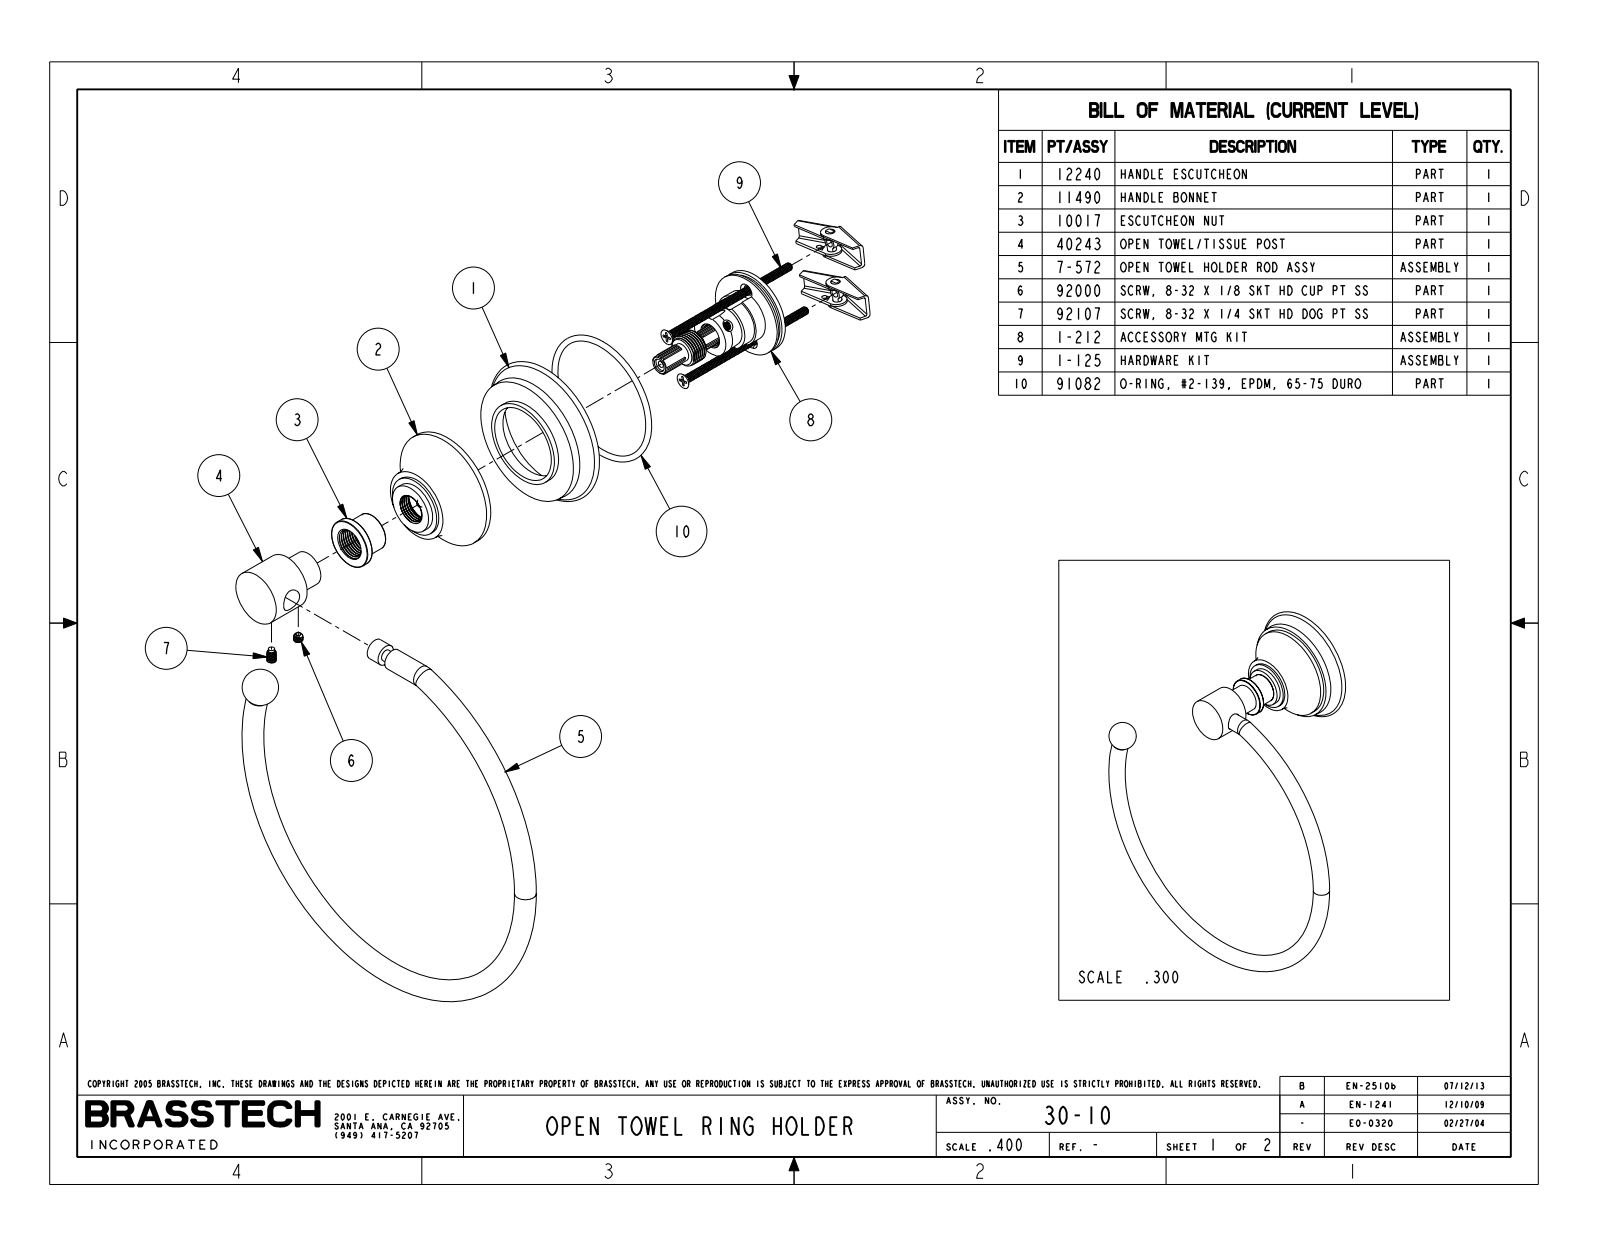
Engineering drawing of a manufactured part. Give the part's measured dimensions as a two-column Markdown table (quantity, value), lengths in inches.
| quantity | value |
| --- | --- |
| part name | 30-10_WEB |
| STEP written by | PRO/ENGINEER BY PARAMETRIC TECHNOLOGY CORPORATION, 2009300 (CONFIG_CONTROL_DESIGN) |
| units | inches |
| bodies | 0 solids, 58 faces (10 planar, 20 cylindrical, 28 other) |
| overall size | 8.125 × 7 × 3.268 |
| round bosses / shafts (diameter × count) | 0.375 × 2, 2.1 × 1, 1.075 × 1, 0.98 × 1, 0.875 × 1, 0.673 × 1, 0.625 × 1 |
| main face-to-face distances | 0.475, 1.225, 0.75, 1.275, 0.8, 0.05, 2.436, 1.961, 1.211, 1.161 |
